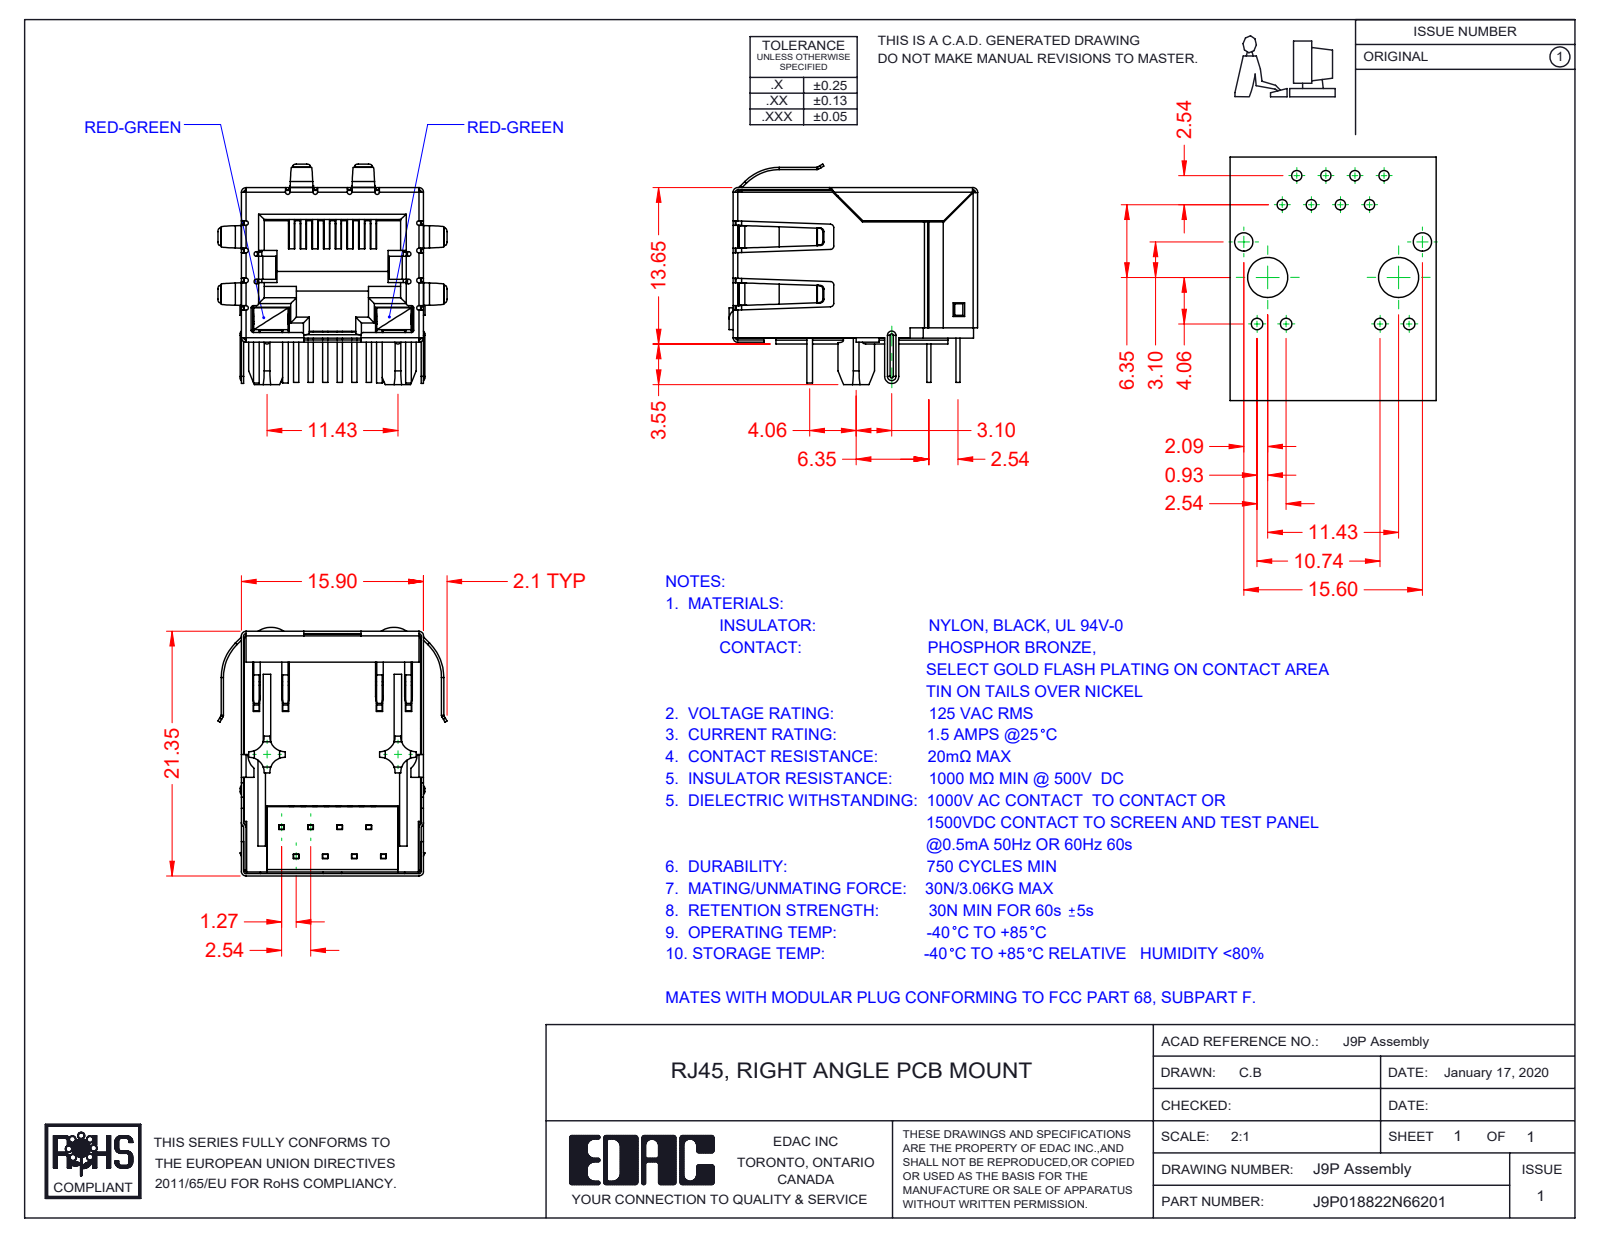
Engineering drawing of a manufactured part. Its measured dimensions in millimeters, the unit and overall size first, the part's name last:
Units: millimetres
Overall size (bounding box): 21.7 × 20 × 19.25
Partial cylindrical surfaces — rounded edges, fillets, slot ends (radius × count): R0.2 ×39, R0.5 ×22, R0.3 ×20, R0.4 ×16, R1.3 ×8, R0.23 ×5, R0.11 ×4, R0.31 ×4
Main face-to-face distances: 15.45, 15.7, 15.65, 0.35, 0.54, 15.5, 12.36, 0.6, 1.4, 0.59
Volume: 2 687 mm³ · Surface area: 7 515 mm²
Bodies: 13 solids, 1476 faces (1042 planar, 340 cylindrical, 94 other)
Part name (STEP PRODUCT): 9P-LED Assembly; 9P-LED LED RH_6-Red-Green; 9P-LED Contacts; 9P-LED Contact Lock (+4 more)
STEP written by: SolidWorks 2016 (CONFIG_CONTROL_DESIGN)
